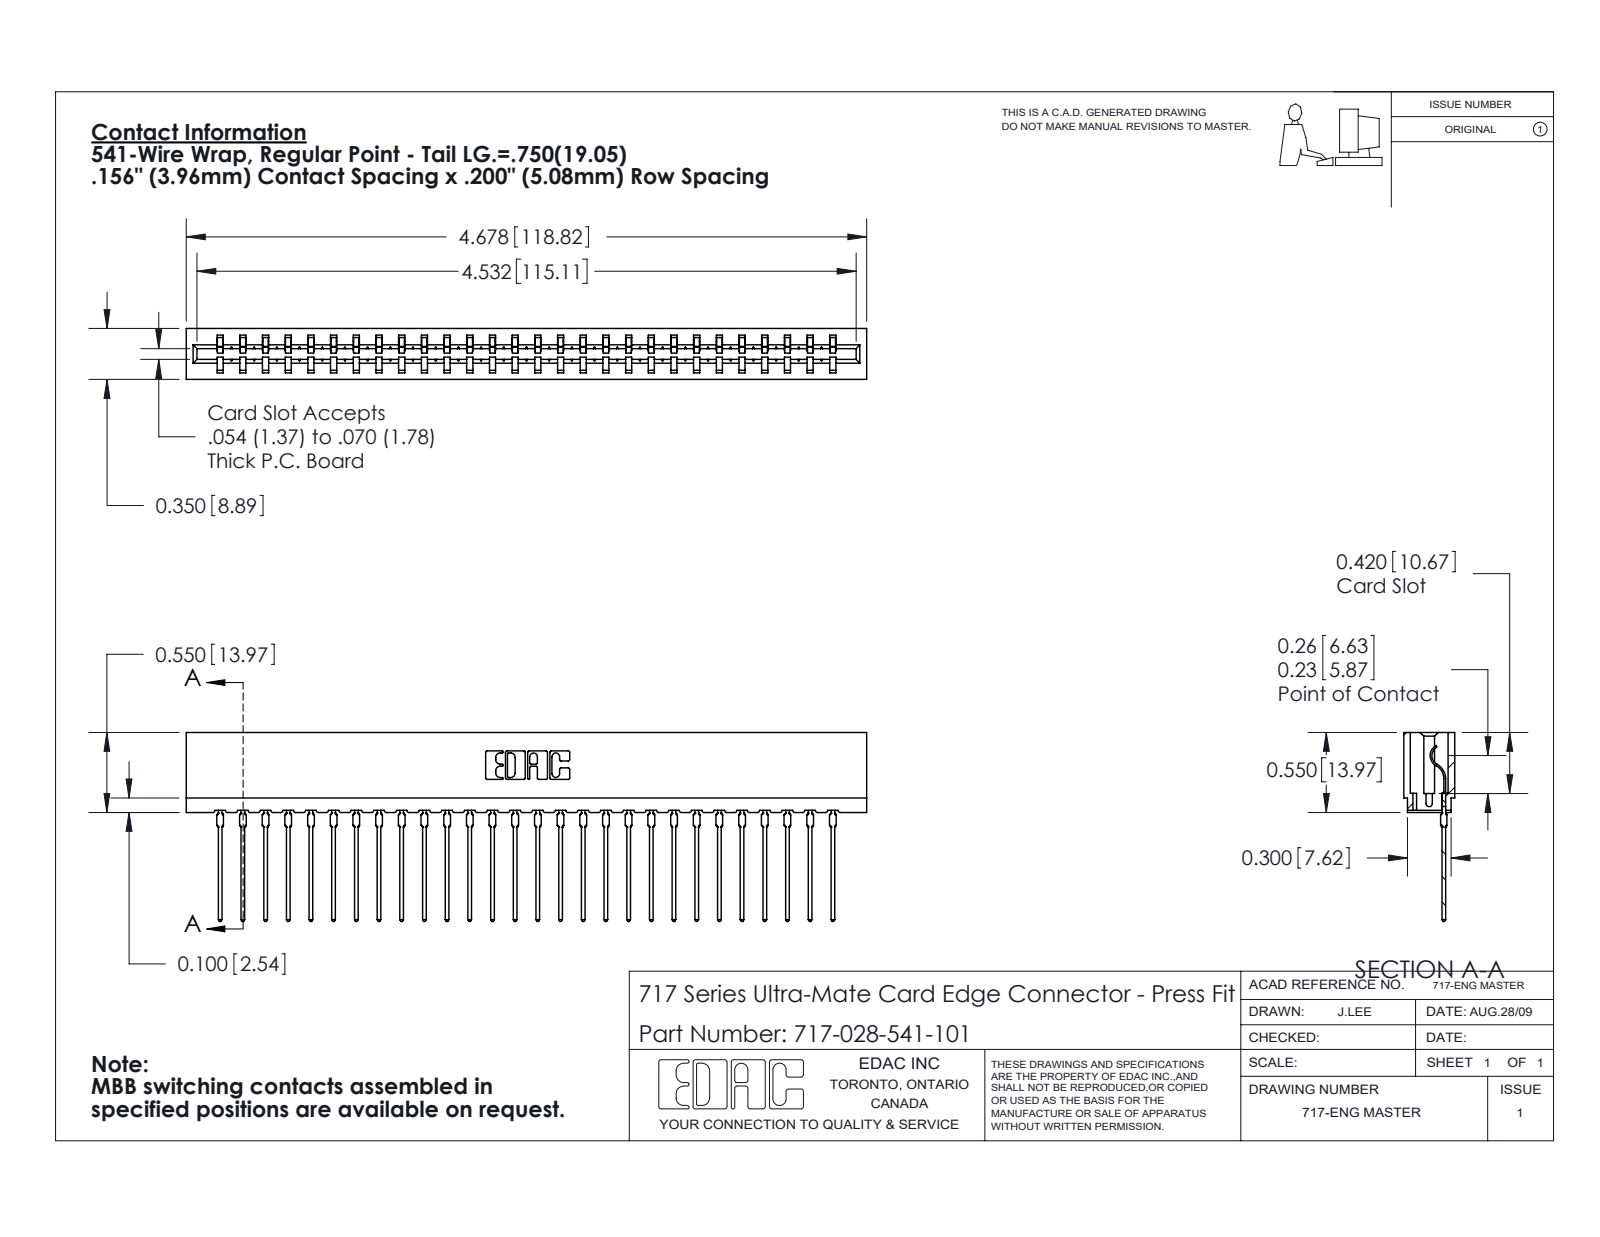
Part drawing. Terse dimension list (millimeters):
name: 717-028-541-101; 745-292-001_541; 717 Part_Insulator Option - 06
written by: SolidWorks 2020 (CONFIG_CONTROL_DESIGN)
unit: mm
bodies: 29 solids, 3258 faces (1958 planar, 572 cylindrical, 728 other)
size: 118.8 × 33 × 8.9
volume: 10 200 mm³; area: 14 790 mm²
rounds: 56× R0.4, 56× R0.5, 22× R0.3, 6× R0.2, 6× R0.8, 4× R0.1, 4× R0.3, 3× R0.7
face distances: 5.4, 3.5, 8.9, 1.6, 7.3, 1.9, 3.8, 1.9, 4, 1.1
